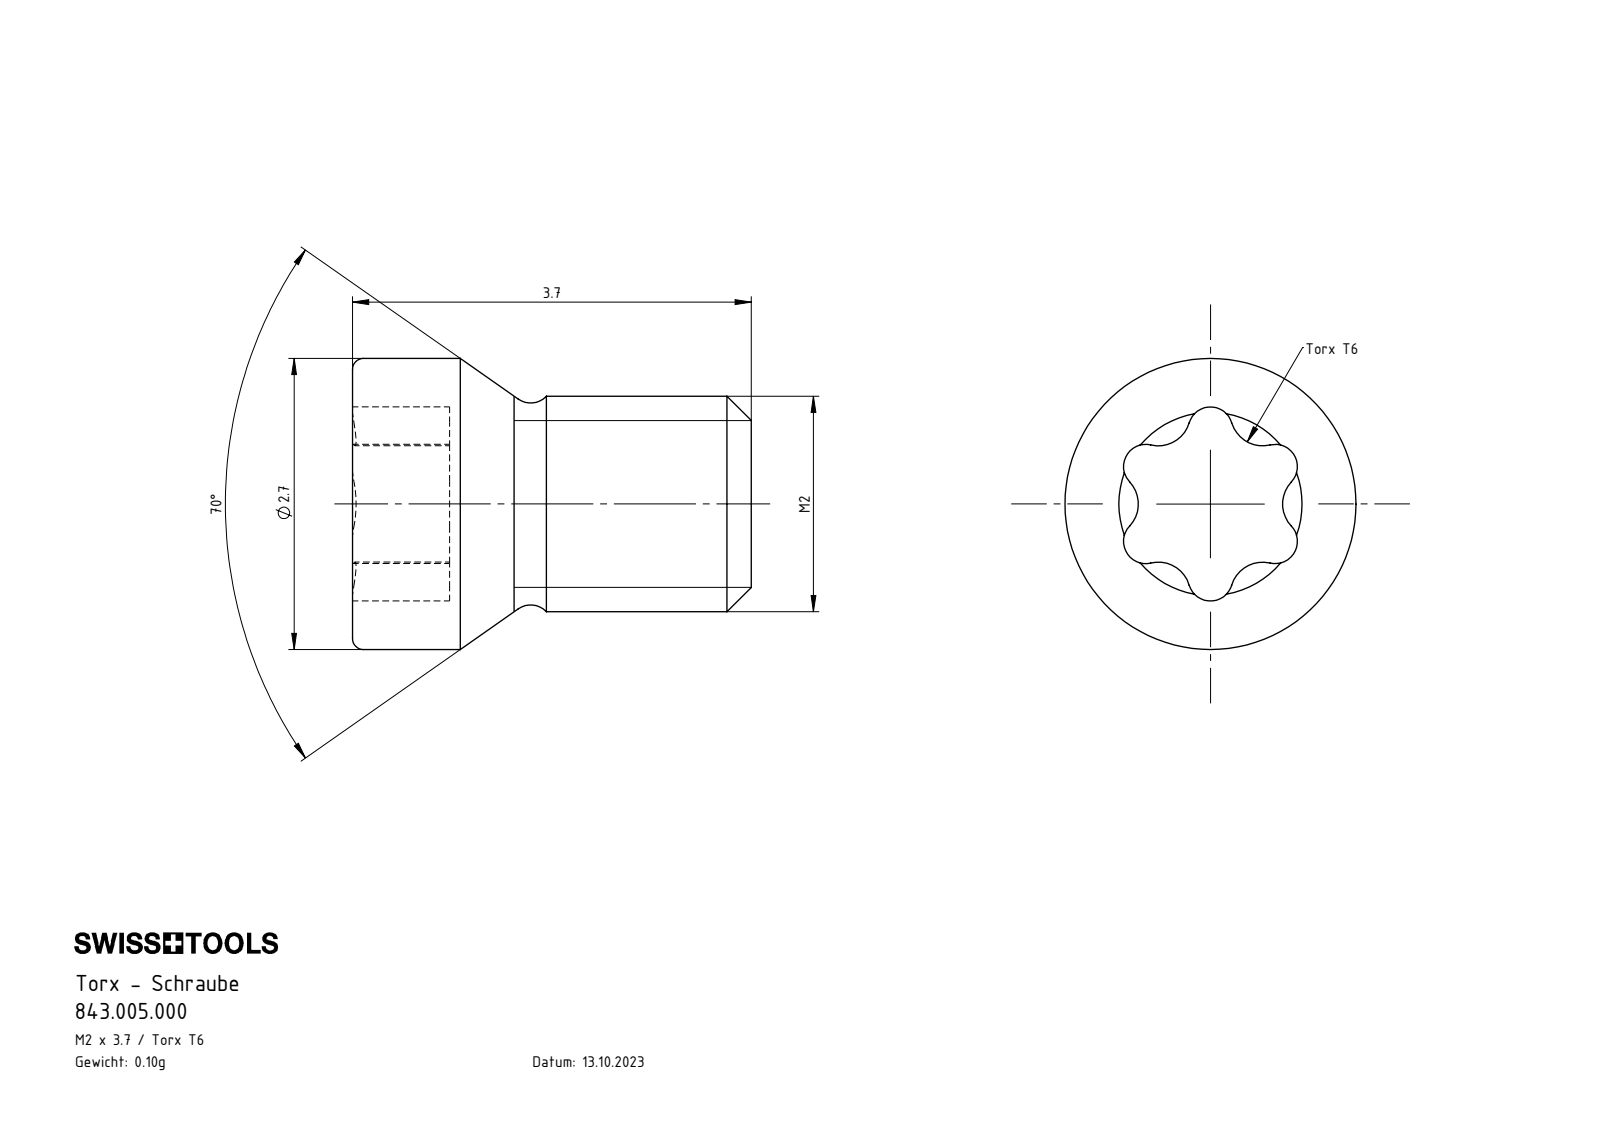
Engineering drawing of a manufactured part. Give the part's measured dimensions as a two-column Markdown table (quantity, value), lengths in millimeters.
| quantity | value |
| --- | --- |
| part name | 843.005.000 |
| STEP written by | SolidWorks 2022 (AUTOMOTIVE_DESIGN) |
| units | millimeters |
| bodies | 1 solid, 41 faces (3 planar, 19 cylindrical, 19 other) |
| overall size | 3.7 × 2.7 × 2.7 |
| volume | 13 mm³ |
| surface area | 40 mm² |
| round bosses / shafts (diameter × count) | 2.7 × 1, 2 × 1 |
| partial cylindrical surfaces (radius × count) | 0.21 × 6, 0.3 × 6 |
| main face-to-face distances | 0.9, 3.7, 2.8 |
